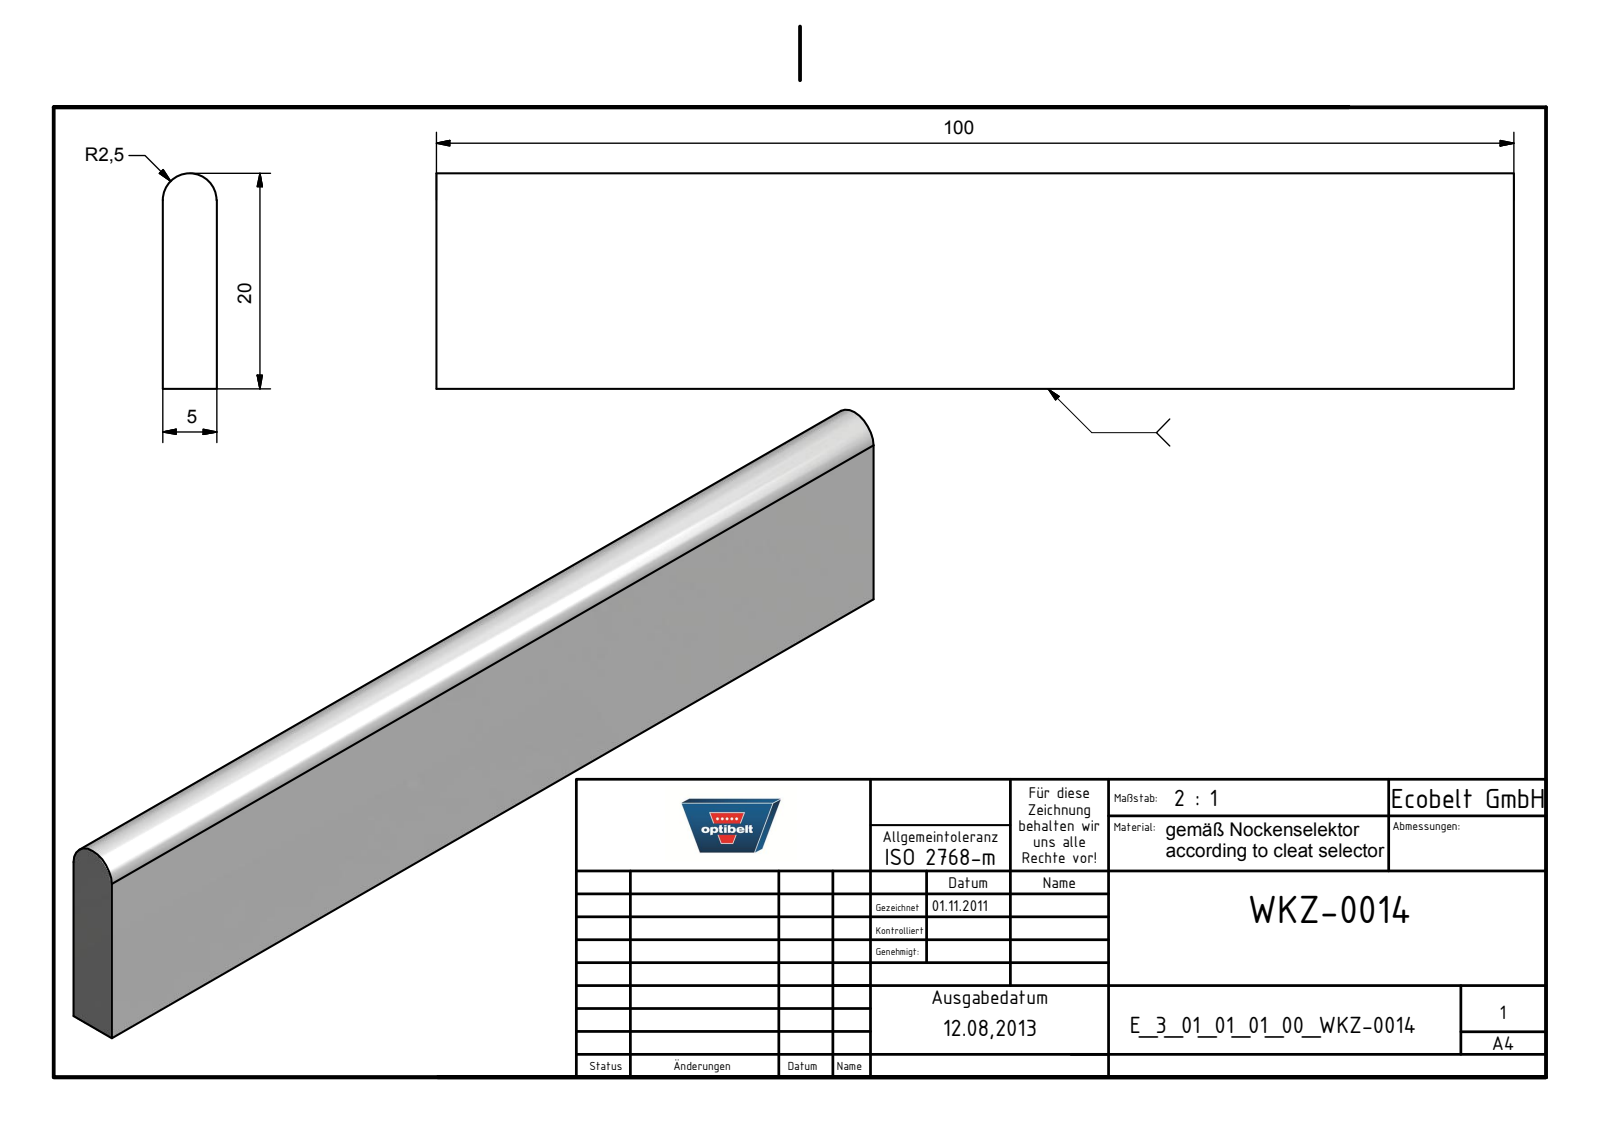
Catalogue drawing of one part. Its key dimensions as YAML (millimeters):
part_name: "E_3_01_01_01_00_WKZ-0014"
step_written_by: "Autodesk Inventor 2021 (AUTOMOTIVE_DESIGN)"
units: millimeters
bodies: {solids: 1, faces: 6, planar: 5, cylindrical: 1, other: 0}
overall_size: [100, 20, 5]
volume: 9732
surface_area: 4980
partial_cylinders:
  - {radius: 2.5, count: 1}
face_to_face_distances: [5, 100]
